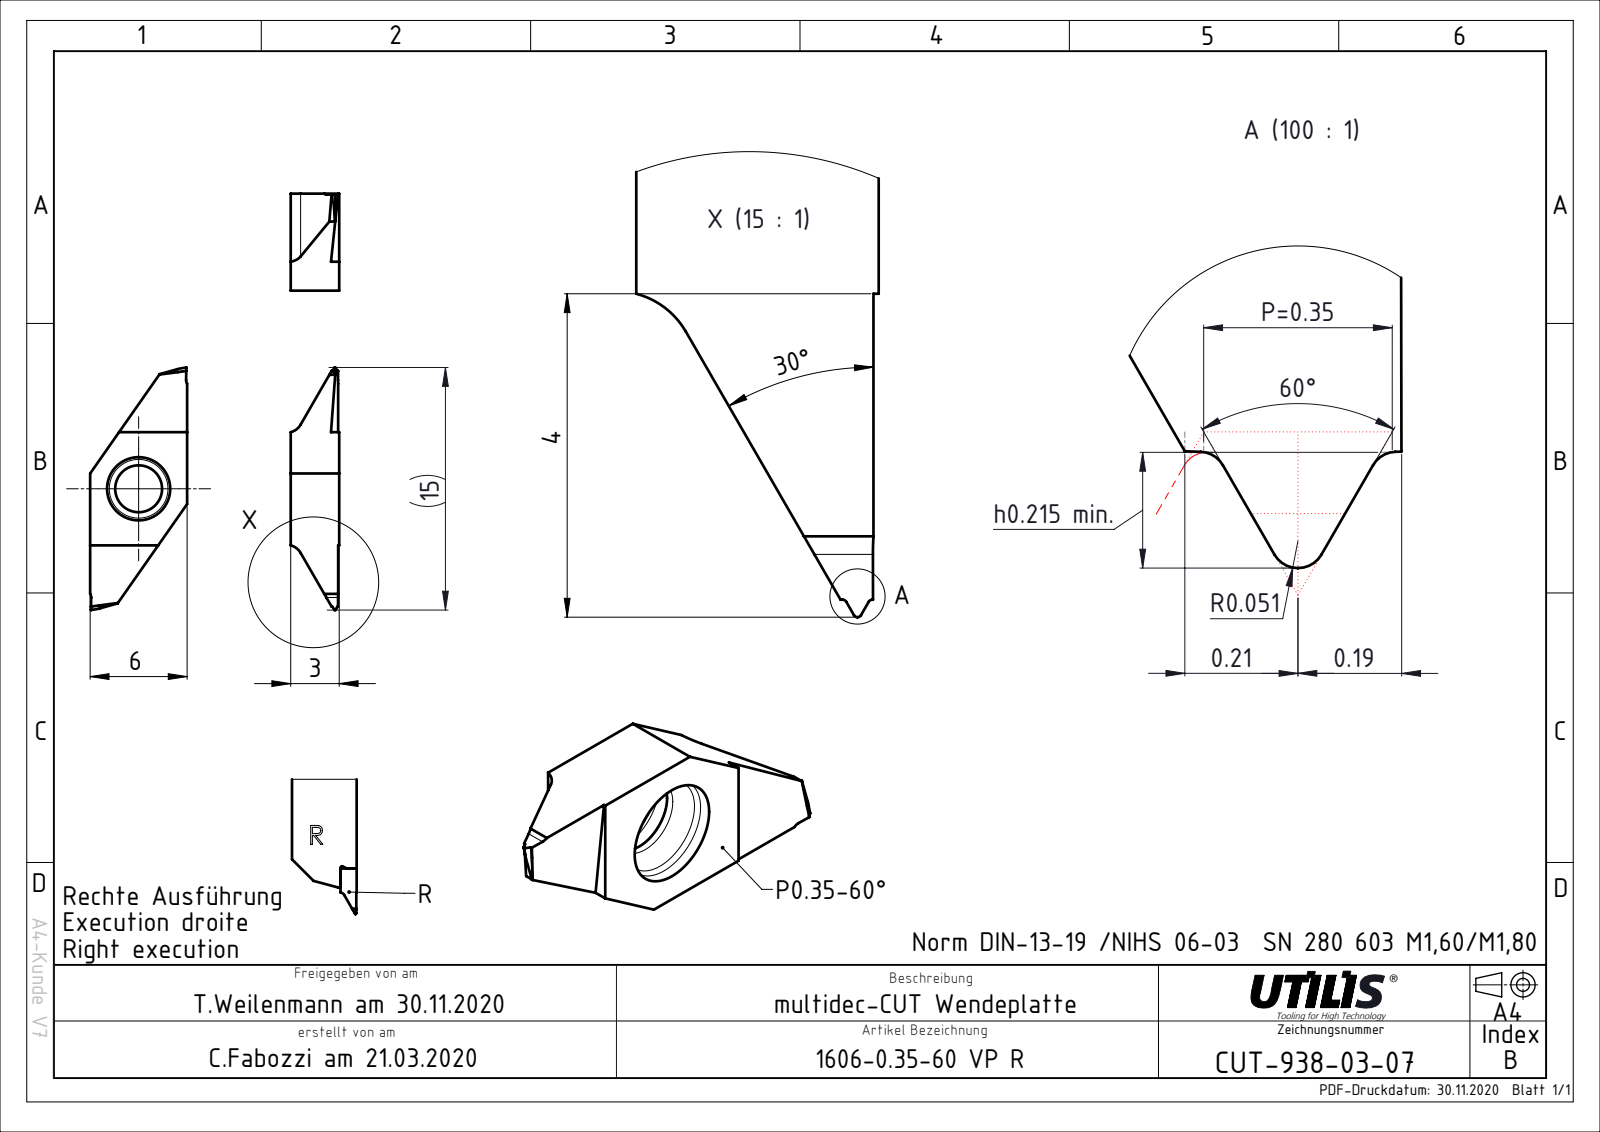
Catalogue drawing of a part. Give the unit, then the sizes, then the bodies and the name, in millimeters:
Units: millimetres
Overall size (bounding box): 15 × 6 × 3
Round holes (diameter × count): ⌀2.9 ×1
Partial cylindrical surfaces — rounded edges, fillets, slot ends (radius × count): R1 ×2
Main face-to-face distances: 6, 3, 9, 11.16, 12, 7, 13.09
Volume: 129 mm³ · Surface area: 211 mm²
Bodies: 1 solid, 40 faces (22 planar, 14 cylindrical, 4 other)
Part name (STEP PRODUCT): CUT-938-03; ASME Y14.5
STEP written by: FormatWorks Professional (AP242_MANAGED_MODEL_BASED_3D_ENGINEERING_MIM_LF)
